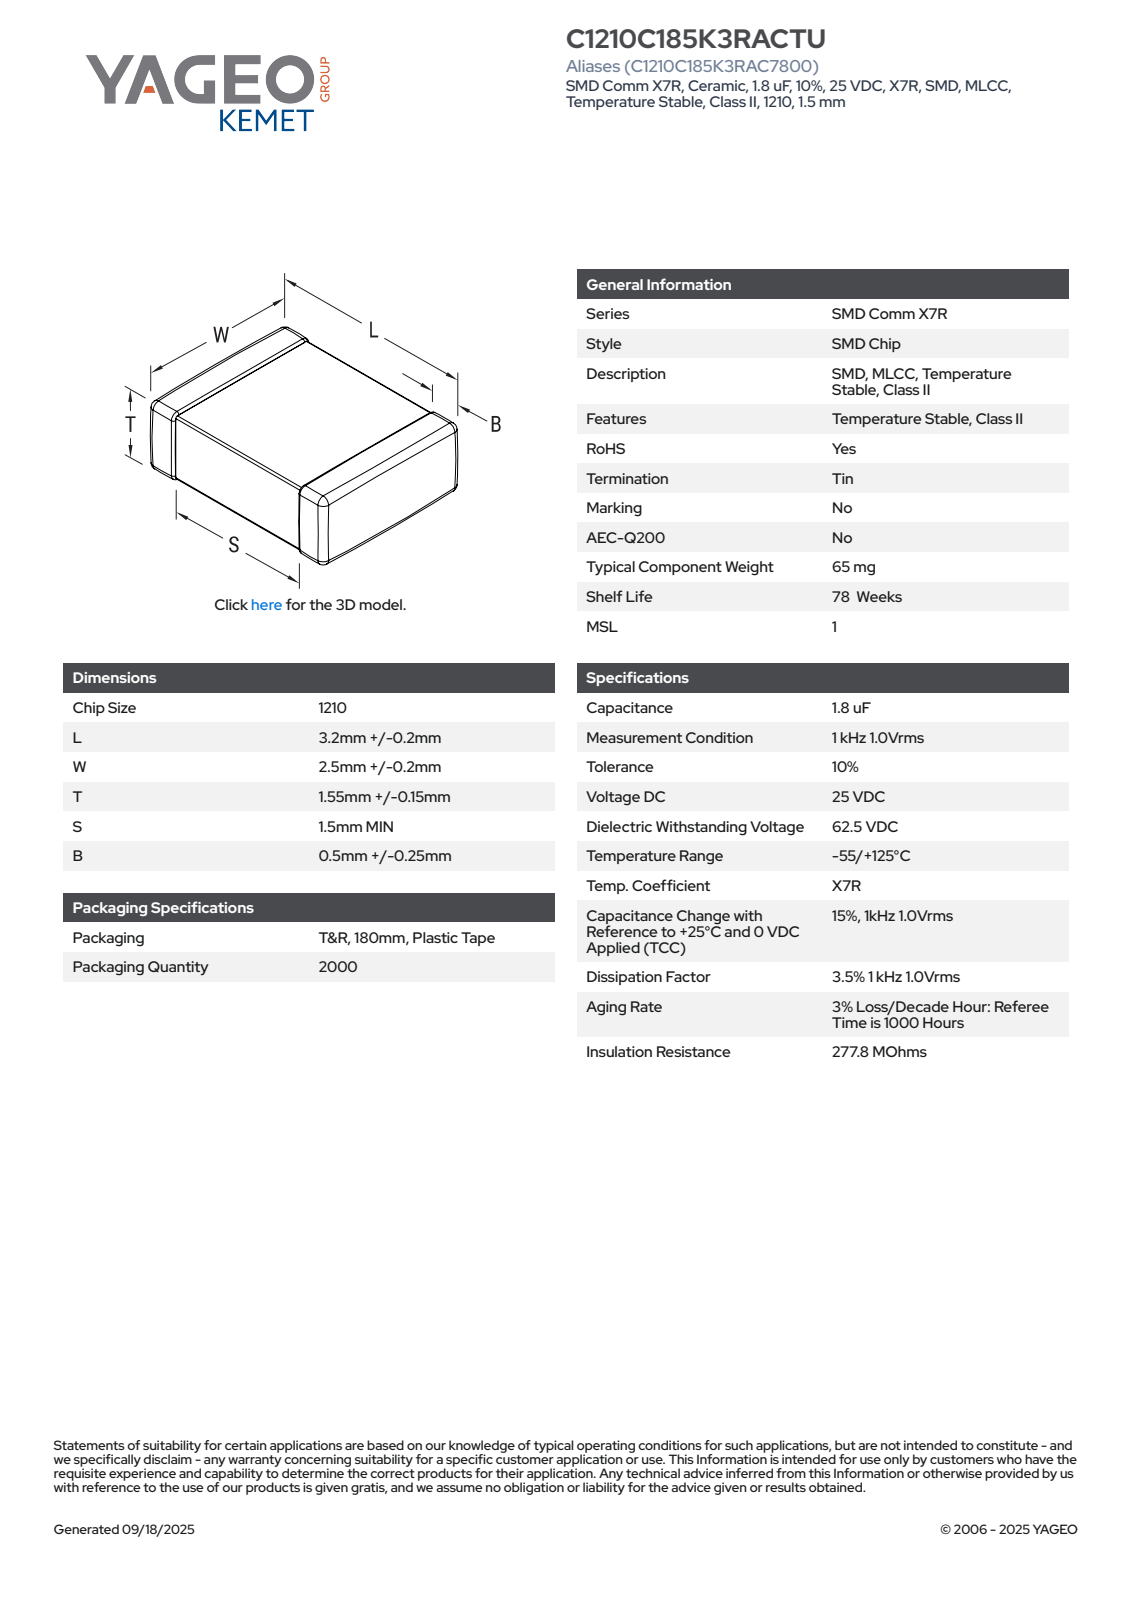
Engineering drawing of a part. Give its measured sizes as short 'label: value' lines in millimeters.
name: CCS_CCSTDNOS_1210_L3.4W2.7T1.7B0.75
written by: SolidWorks 2014 (AUTOMOTIVE_DESIGN)
unit: mm
bodies: 4 solids, 125 faces (71 planar, 38 cylindrical, 16 other)
size: 3.4 × 2.7 × 1.7
volume: 15 mm³; area: 38 mm²
face distances: 1.64, 1.58, 3.4, 2.64, 1.7, 2.58, 2.7, 1.65, 1.59, 1.31
